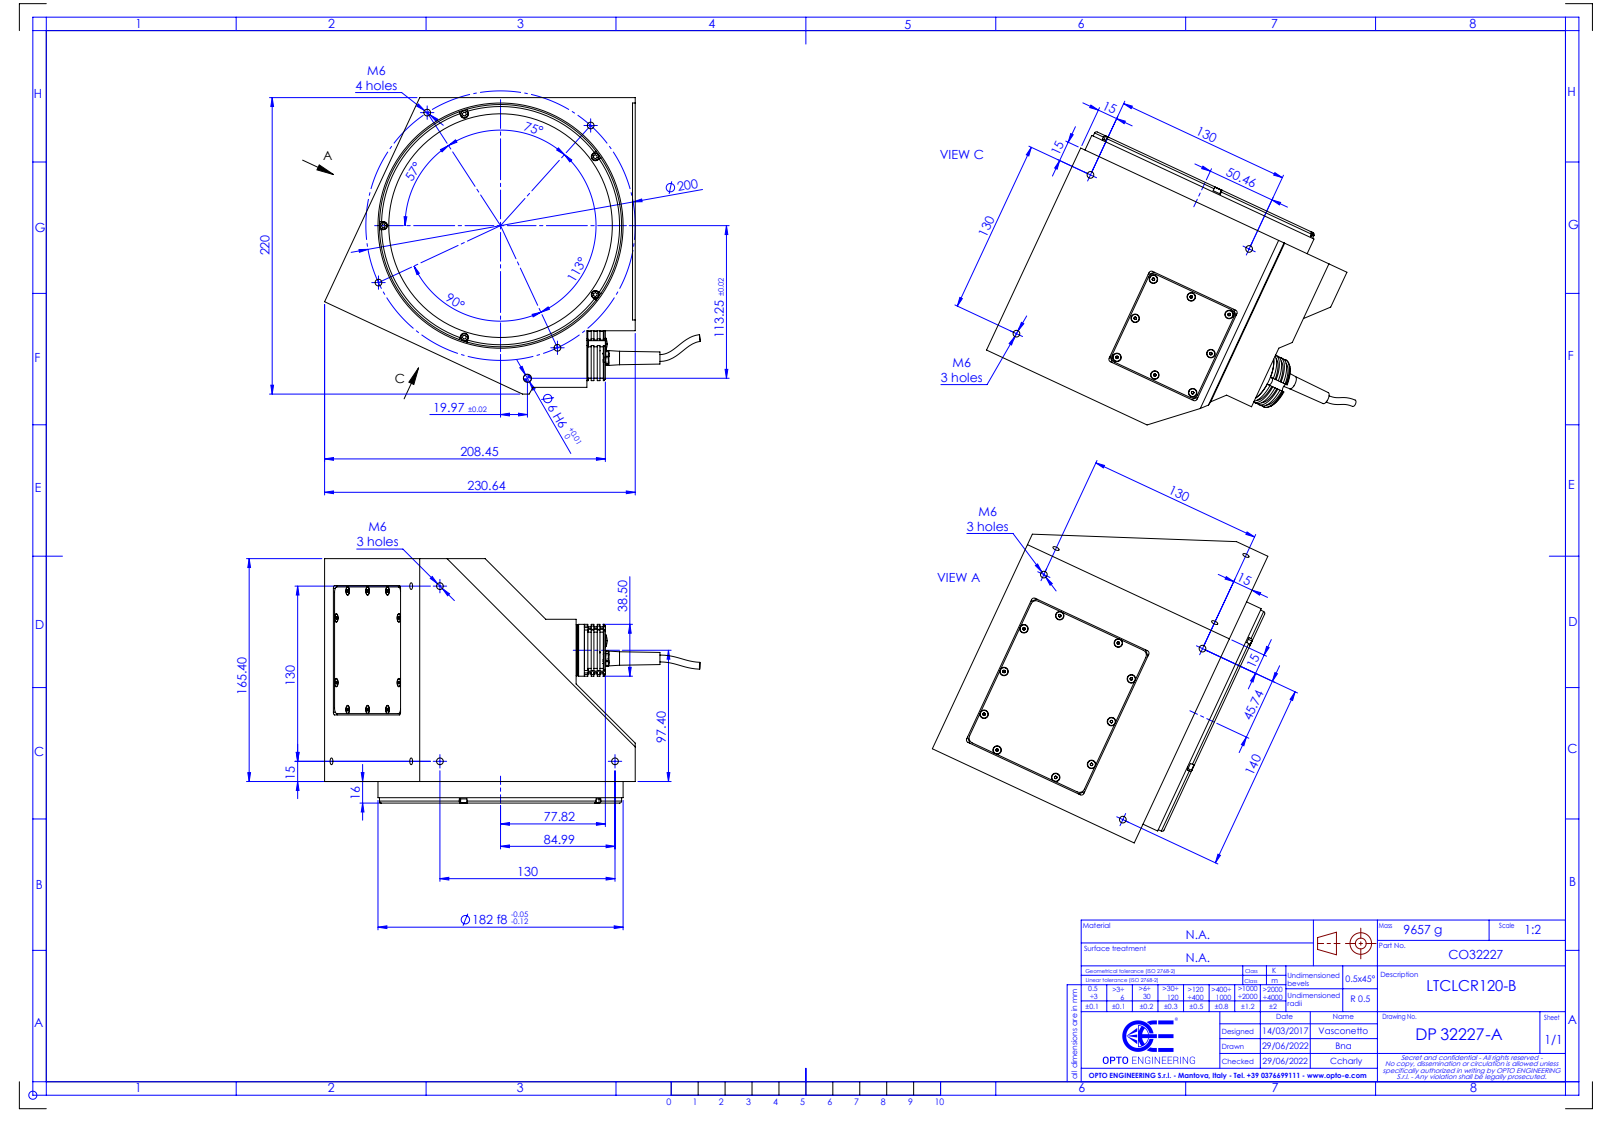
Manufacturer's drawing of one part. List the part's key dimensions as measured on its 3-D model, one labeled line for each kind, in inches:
Part name (STEP PRODUCT): DP32227-A_LTCLCR120-B
STEP written by: SolidWorks 2021 (CONFIG_CONTROL_DESIGN)
Units: inches
Bodies: 0 solids, 582 faces (245 planar, 174 cylindrical, 163 other)
Overall size (bounding box): 10.981 × 8.661 × 7.142
Round holes (diameter × count): ⌀0.197 ×13, ⌀0.157 ×3, ⌀0.236 ×1, ⌀6.535 ×1, ⌀6.724 ×1
Round bosses / shafts (diameter × count): ⌀0.226 ×25, ⌀0.217 ×8, ⌀7.165 ×1, ⌀7.079 ×1, ⌀1.516 ×1, ⌀1.488 ×1, ⌀1.374 ×1
Partial cylindrical surfaces — rounded edges, fillets, slot ends (radius × count): R0.157 ×10, R0.079 ×8, R0.118 ×5, R0.114 ×3, R0.134 ×1
Main face-to-face distances: 6.512, 0.017, 0.079, 0.022, 8.465, 6.496, 1.969, 0.157, 0.315, 0.787
Hole centre spacings: 5.118, 3.937, 1.04, 1.04, 1.25, 3.937, 4.528, 4.793
